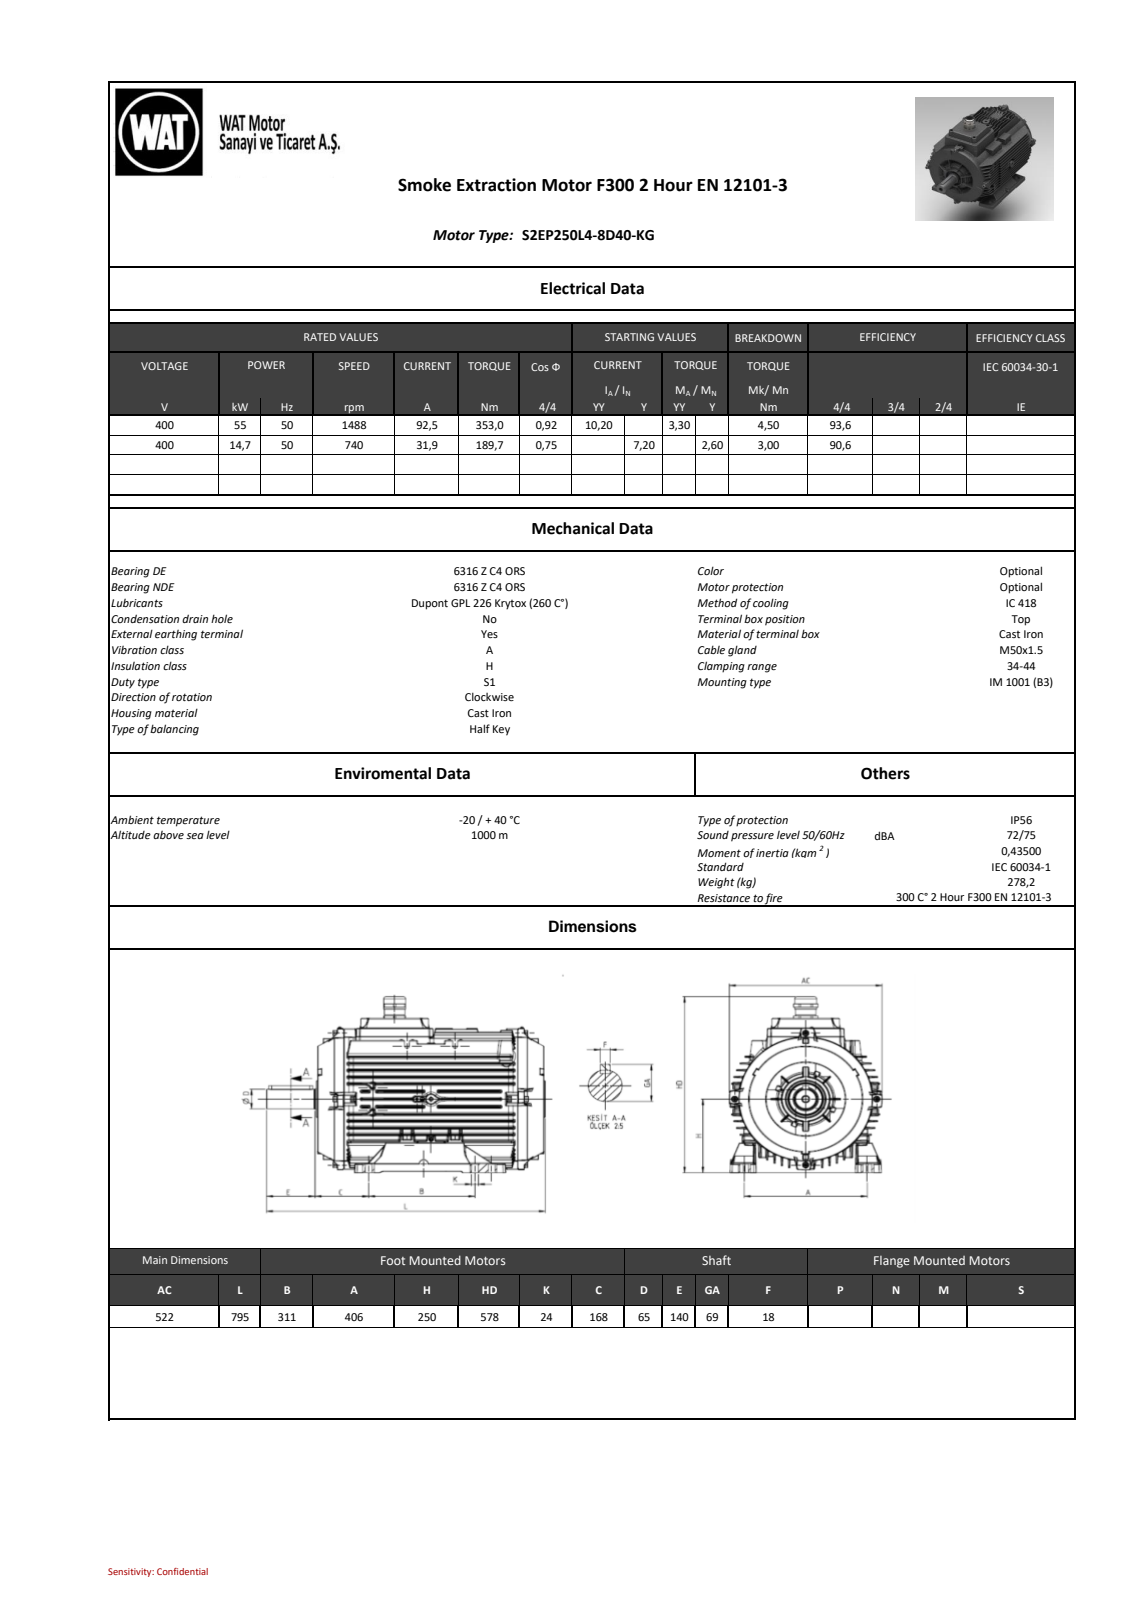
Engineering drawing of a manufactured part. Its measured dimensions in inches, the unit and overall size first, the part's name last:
Units: inches
Overall size (bounding box): 31.283 × 22.748 × 20.551
Round holes (diameter × count): ⌀0.315 ×4, ⌀0.827 ×4, ⌀0.787 ×3, ⌀0.276 ×2, ⌀0.63 ×2, ⌀3.937 ×2, ⌀0.394 ×1, ⌀1.732 ×1, ⌀3.228 ×1, ⌀3.772 ×1, ⌀5.866 ×1
Round bosses / shafts (diameter × count): ⌀1.079 ×4, ⌀7.289 ×2, ⌀3.15 ×1, ⌀2.559 ×1, ⌀2.48 ×1, ⌀2.362 ×1, ⌀2.329 ×1, ⌀2.269 ×1
Partial cylindrical surfaces — rounded edges, fillets, slot ends (radius × count): R0.039 ×98, R0.197 ×61, R0.079 ×39, R0.118 ×27, R0.394 ×7, R0.787 ×6, R0.591 ×5, R0.539 ×4
Main face-to-face distances: 9.731, 0.791, 1.378, 0.686, 9.836, 0.105, 9.046, 0.688, 1.374, 9.148
Hole centre spacings: 4.317, 5.221, 5.906, 6.299, 8.635, 8.799, 11.009, 0.033
Bodies: 0 solids, 2260 faces (1211 planar, 480 cylindrical, 569 other)
Part name (STEP PRODUCT): 2603EC1454FFjkxs
STEP written by: SIEMENS PLM Software NX 11.0 (AUTOMOTIVE_DESIGN)
